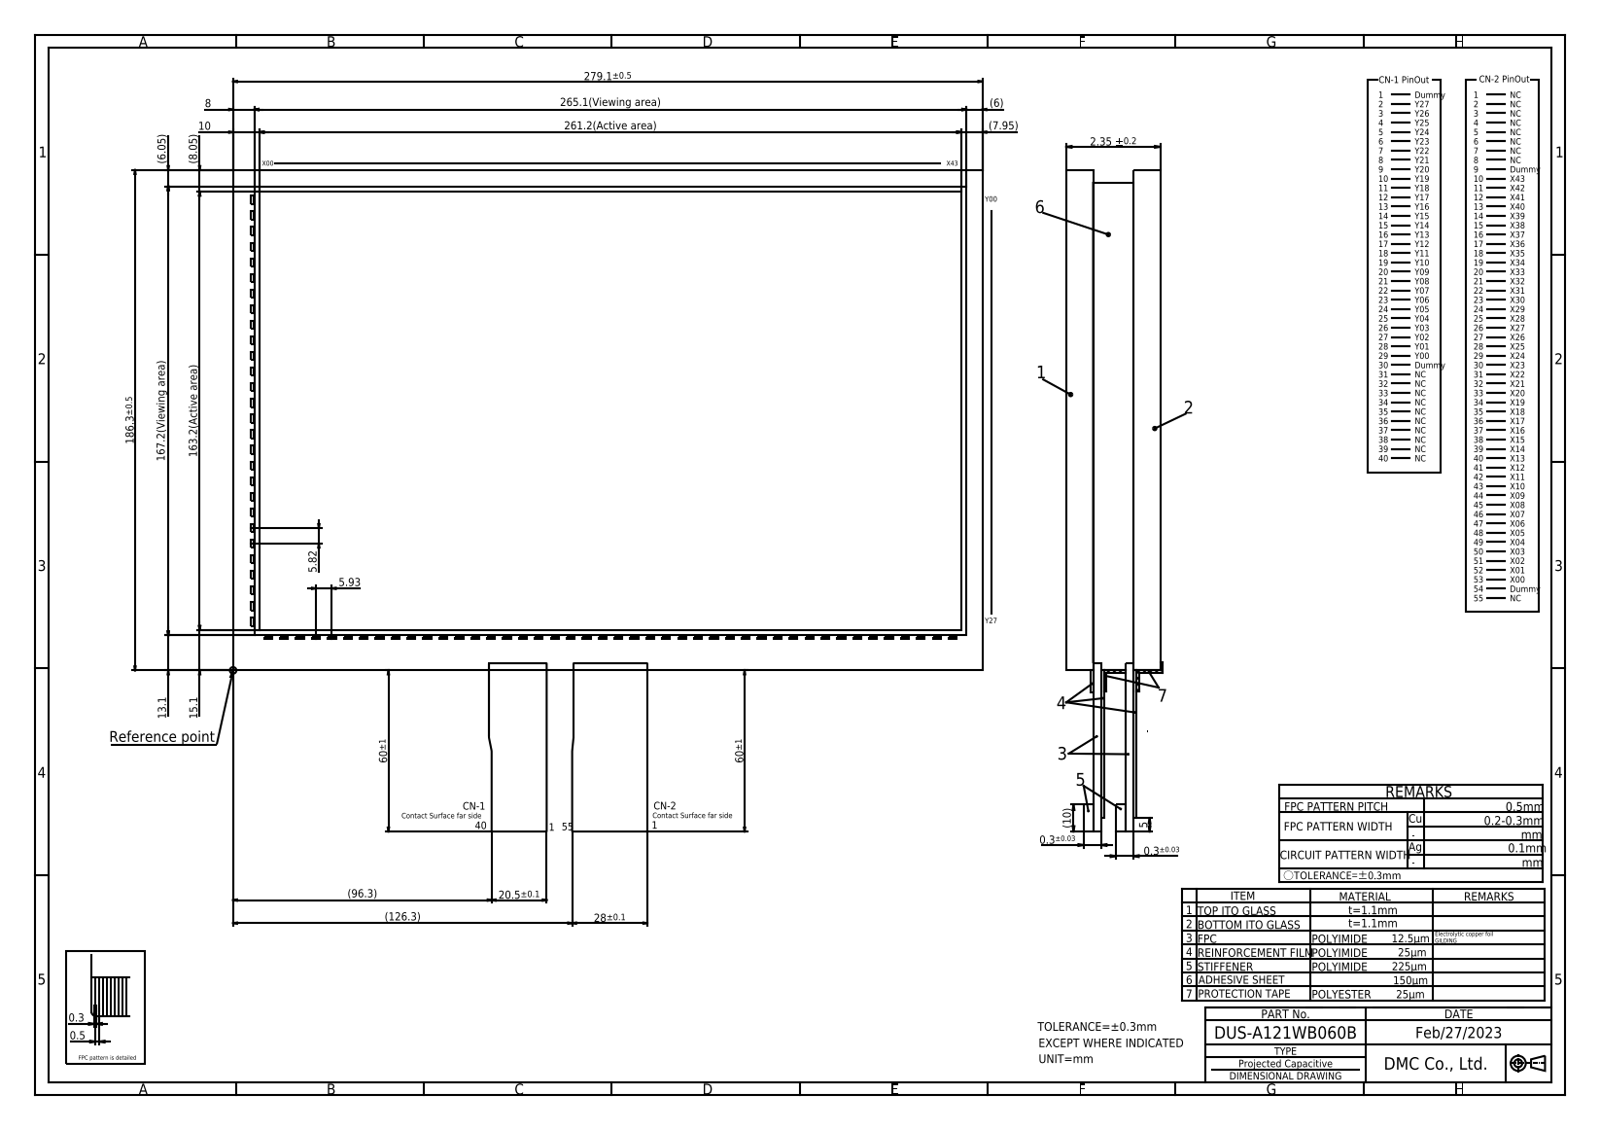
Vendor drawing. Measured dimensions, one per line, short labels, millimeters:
name: DUS-A121WB060B
written by: Autodesk Inventor 2020 (CONFIG_CONTROL_DESIGN)
unit: mm
bodies: 1 solid, 422 faces (418 planar, 4 cylindrical, 0 other)
size: 390.74 × 283.56 × 2.35
volume: 122 434 mm³; area: 112 271 mm²
rounds: 4× R0.2
face distances: 2.35, 1.1, 1.15, 1.2, 1.25, 1, 2.25, 186.3, 0.8, 0.7
